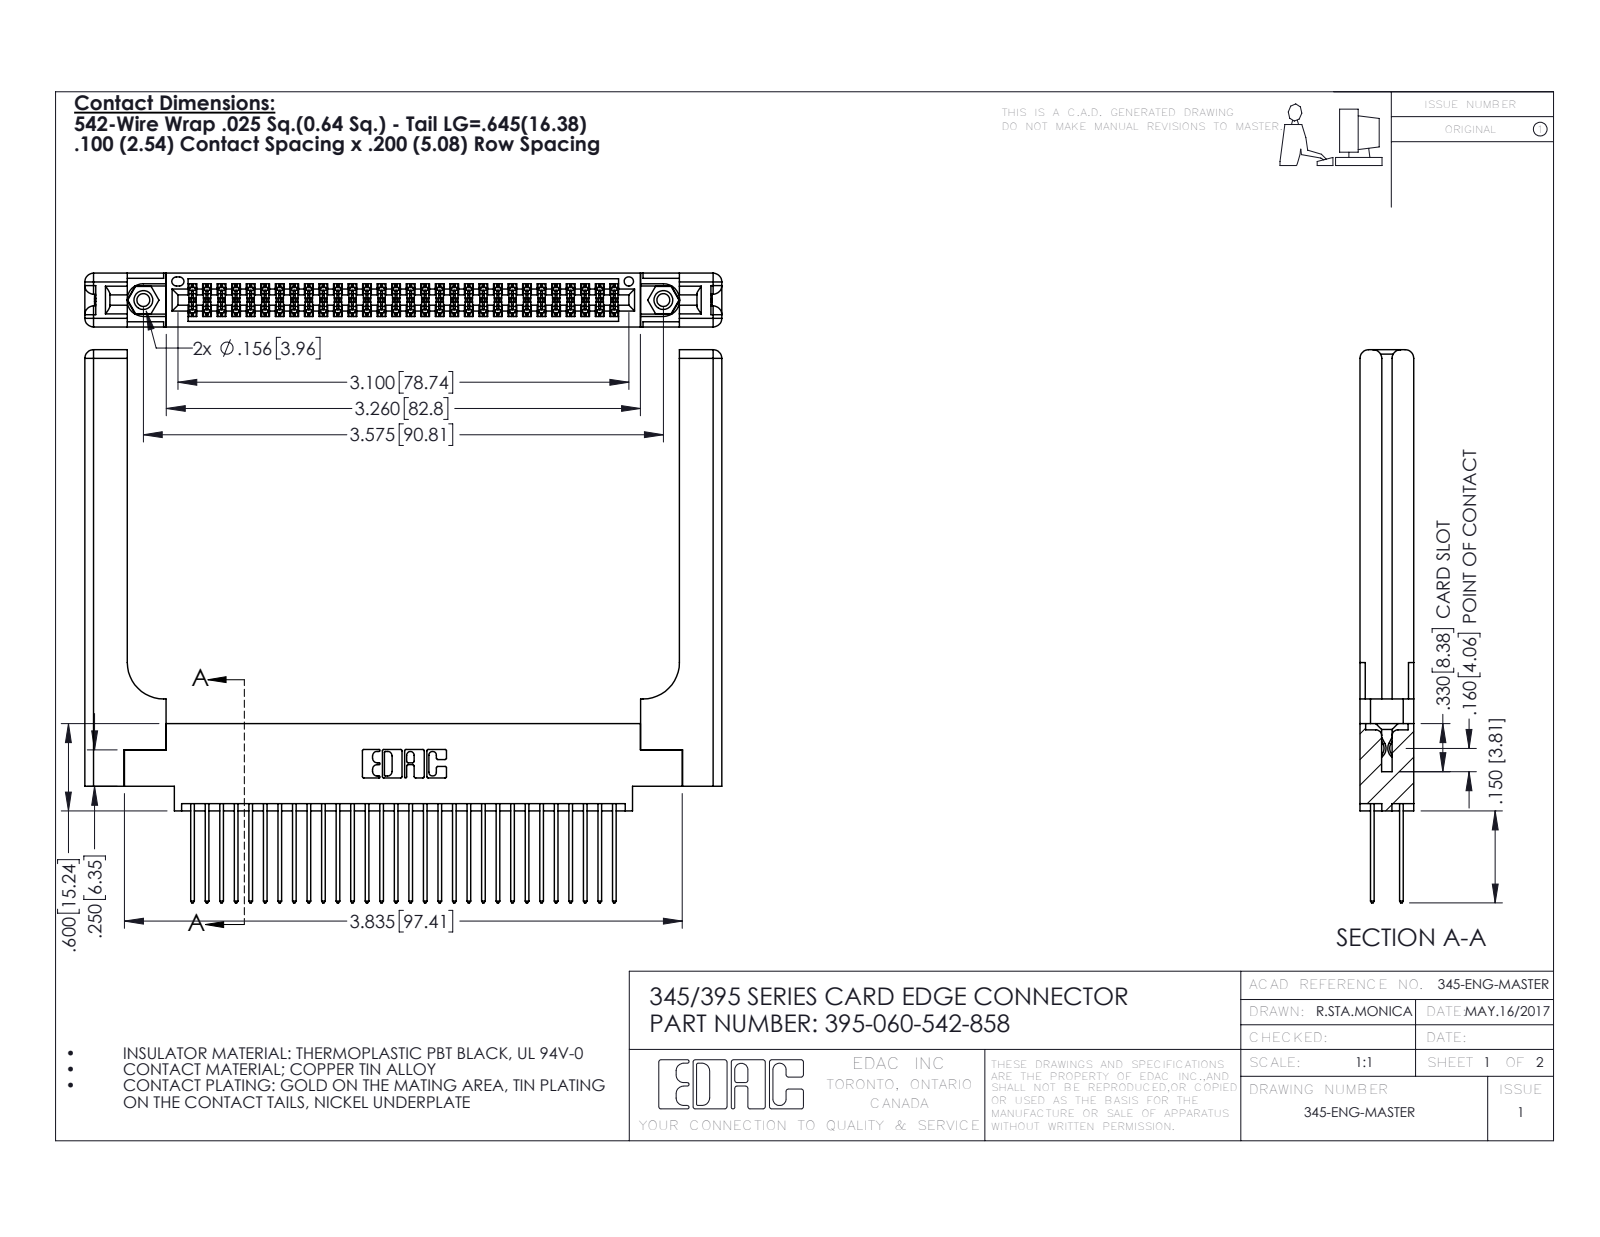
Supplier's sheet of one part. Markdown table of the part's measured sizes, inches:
| quantity | value |
| --- | --- |
| part name | 345-250-001_345-250-001-102; 345-220-058_345-220-058; 345 Part_0.170 Offset - 0.156 Dia-TH; 395-060-542-858 (+1 more) |
| STEP written by | SolidWorks 2016 (CONFIG_CONTROL_DESIGN) |
| units | inches |
| bodies | 65 solids, 3386 faces (2212 planar, 1114 cylindrical, 60 other) |
| overall size | 4.379 × 3.802 × 0.37 |
| volume | 1.18 in³ |
| surface area | 34.61 in² |
| round holes (diameter × count) | 0.089 × 2, 0.125 × 2, 0.156 × 2, 0.064 × 1 |
| round bosses / shafts (diameter × count) | 0.155 × 2 |
| partial cylindrical surfaces (radius × count) | 0.006 × 90, 0.01 × 60, 0.01 × 22, 0.06 × 16, 0.007 × 6, 0.031 × 6, 0.026 × 3, 0.014 × 2 |
| main face-to-face distances | 0.072, 0.298, 0.37, 0.098, 0.272, 0.025, 0.2, 0.225, 0.175, 0.148 |
| hole center spacings | 0.27, 3.34, 3.575 |
